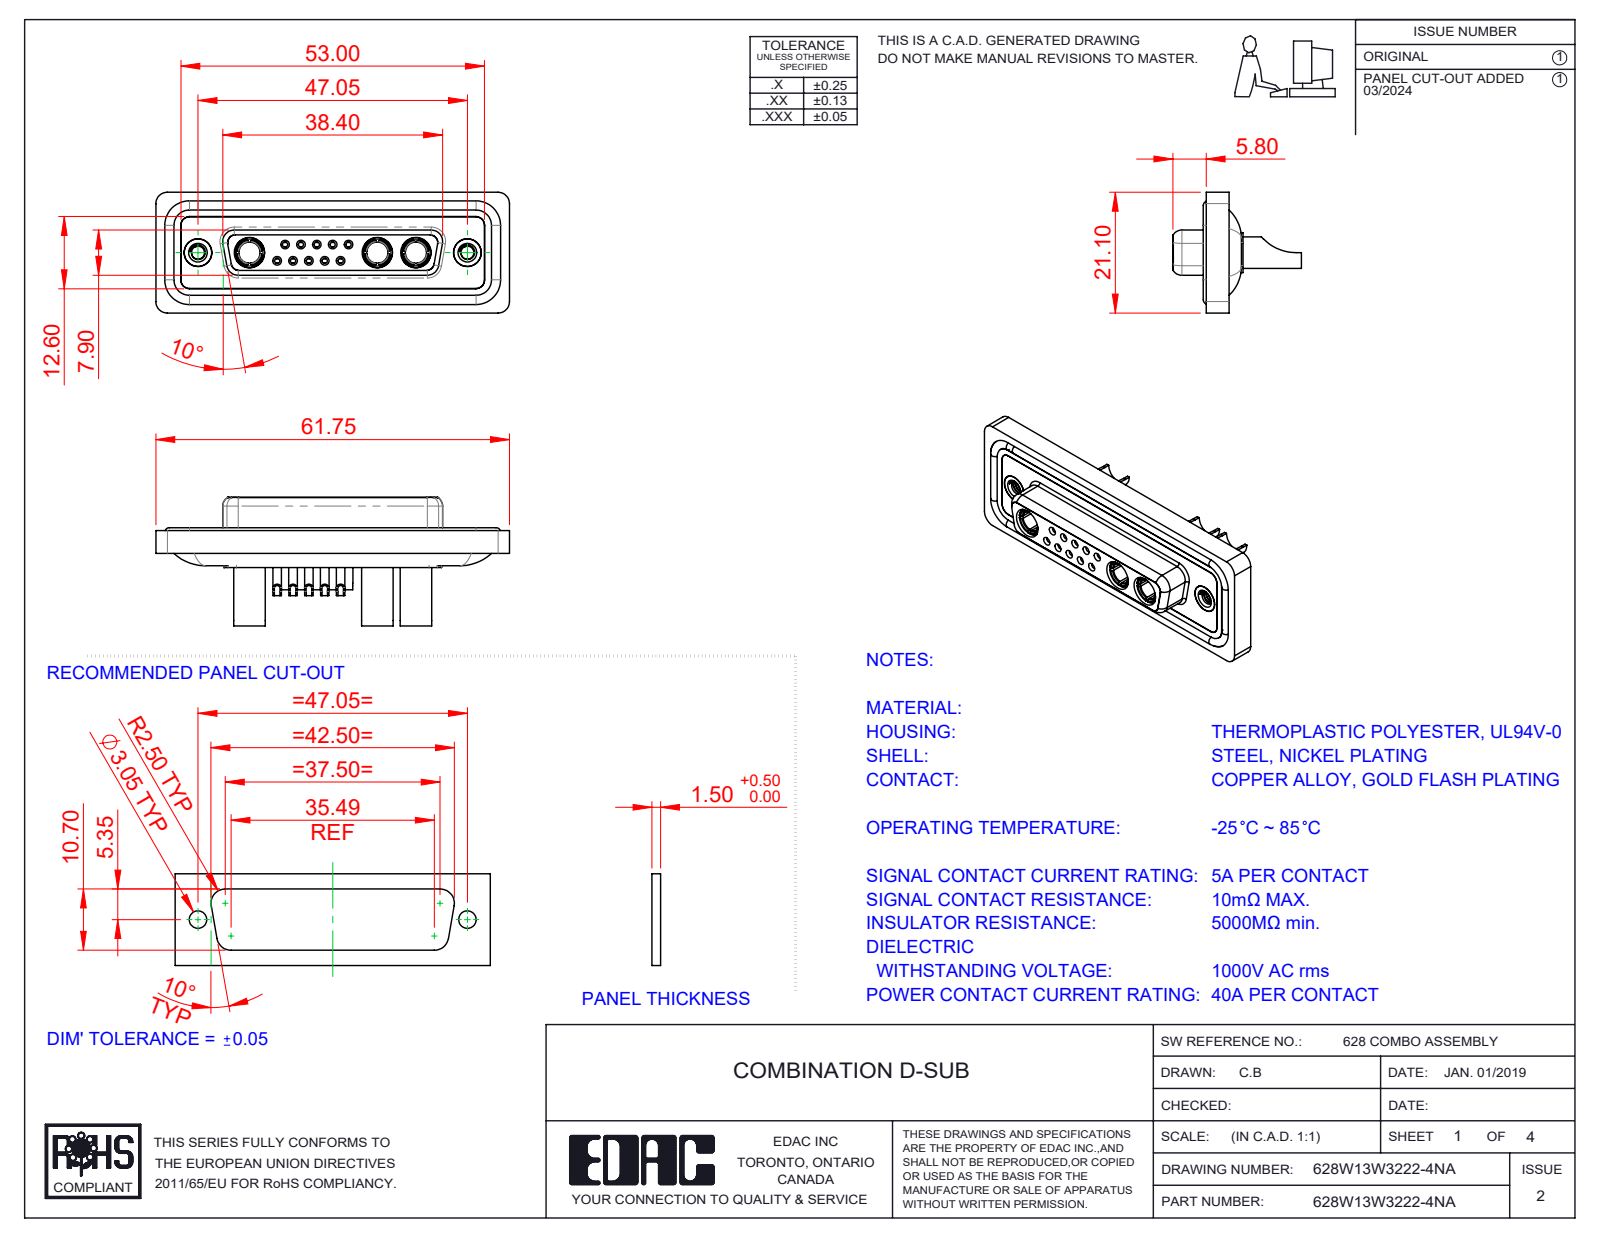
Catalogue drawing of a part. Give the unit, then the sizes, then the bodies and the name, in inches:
Units: inches
Overall size (bounding box): 2.431 × 0.884 × 0.831
Round holes (diameter × count): ⌀0.035 ×10, ⌀0.039 ×10, ⌀0.043 ×10, ⌀0.059 ×10, ⌀0.079 ×10, ⌀0.063 ×5, ⌀0.067 ×5, ⌀0.191 ×5, ⌀0.146 ×3, ⌀0.181 ×3, ⌀0.209 ×3, ⌀0.089 ×2
Round bosses / shafts (diameter × count): ⌀0.087 ×10, ⌀0.063 ×9, ⌀0.217 ×3, ⌀0.205 ×3, ⌀0.195 ×3, ⌀0.187 ×3, ⌀0.148 ×3, ⌀0.195 ×2
Partial cylindrical surfaces — rounded edges, fillets, slot ends (radius × count): R0.059 ×22, R0.079 ×18, R0.053 ×8, R0.063 ×8, R0.039 ×6, R0.01 ×4, R0.02 ×4, R0.024 ×4
Main face-to-face distances: 0.016, 0.293, 0.071, 0.222, 0.02, 0.26, 0.278, 0.063, 0.114, 0.043
Hole centre spacings: 0.124, 0.109, 0.198, 0.198, 0.218, 0.327, 0.295, 0.109
Volume: 0.514 in³ · Surface area: 22.06 in²
Bodies: 23 solids, 1165 faces (368 planar, 472 cylindrical, 325 other)
Part name (STEP PRODUCT): 628W13W3222-4NA; 628Combo Contact Row 2_22; 628Combo Housing_13W3; 628Combo Threaded Rivet_A (+5 more)
STEP written by: SolidWorks 2023 (CONFIG_CONTROL_DESIGN)
